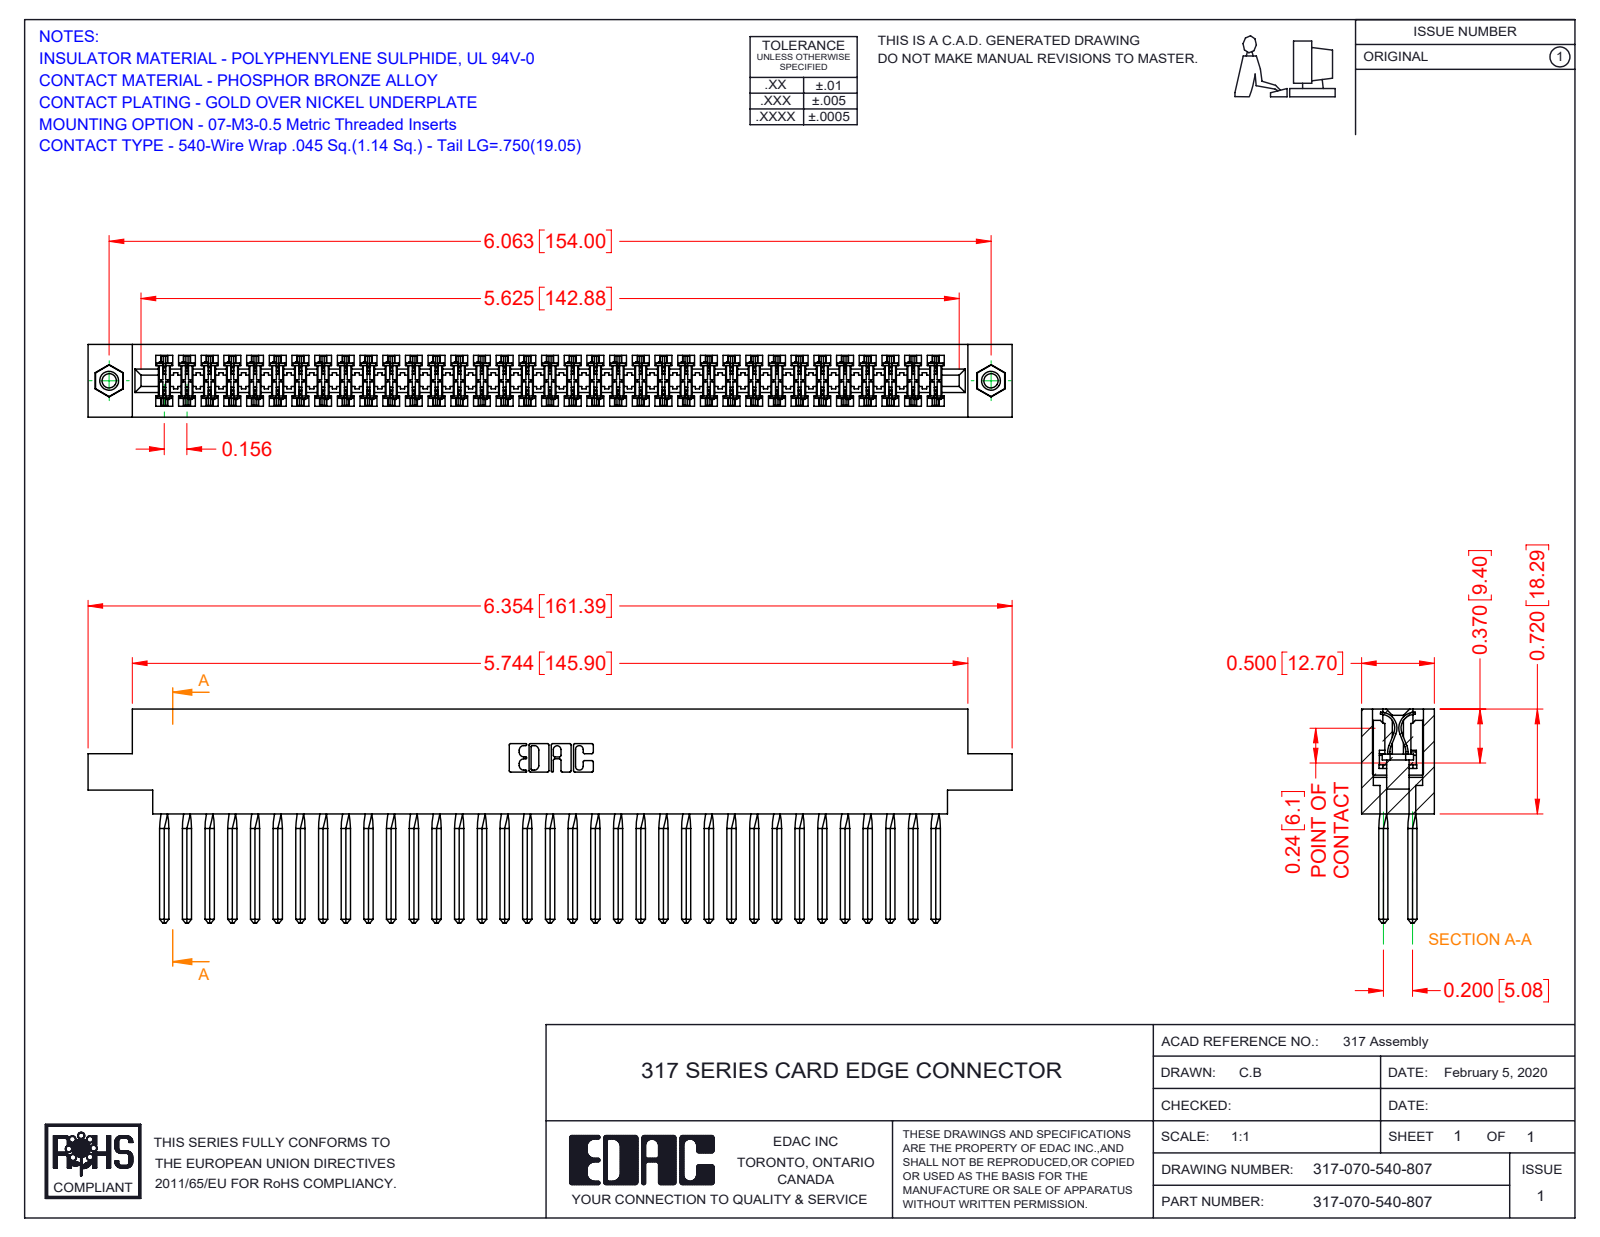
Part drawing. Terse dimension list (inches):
name: 317-070-540-807; 317 Part_.156 Dia - TI; 317-290-001_540; 345-250-001_345-250-005-103
written by: SolidWorks 2016 (CONFIG_CONTROL_DESIGN)
unit: in
bodies: 73 solids, 6392 faces (5200 planar, 896 cylindrical, 296 other)
size: 6.354 × 1.47 × 0.5
volume: 1.638 in³; area: 61.66 in²
holes: 2× ⌀0.098, 2× ⌀0.125, 2× ⌀0.156
bosses: 2× ⌀0.155
rounds: 140× R0.015, 22× R0.01, 6× R0.007, 6× R0.031, 3× R0.026, 2× R0.095, 2× R0.1, 2× R0.11
face distances: 0.5, 0.075, 0.425, 0.35, 0.195, 0.11, 0.094, 0.2, 0.115, 0.131
hole spacings: 6.063
